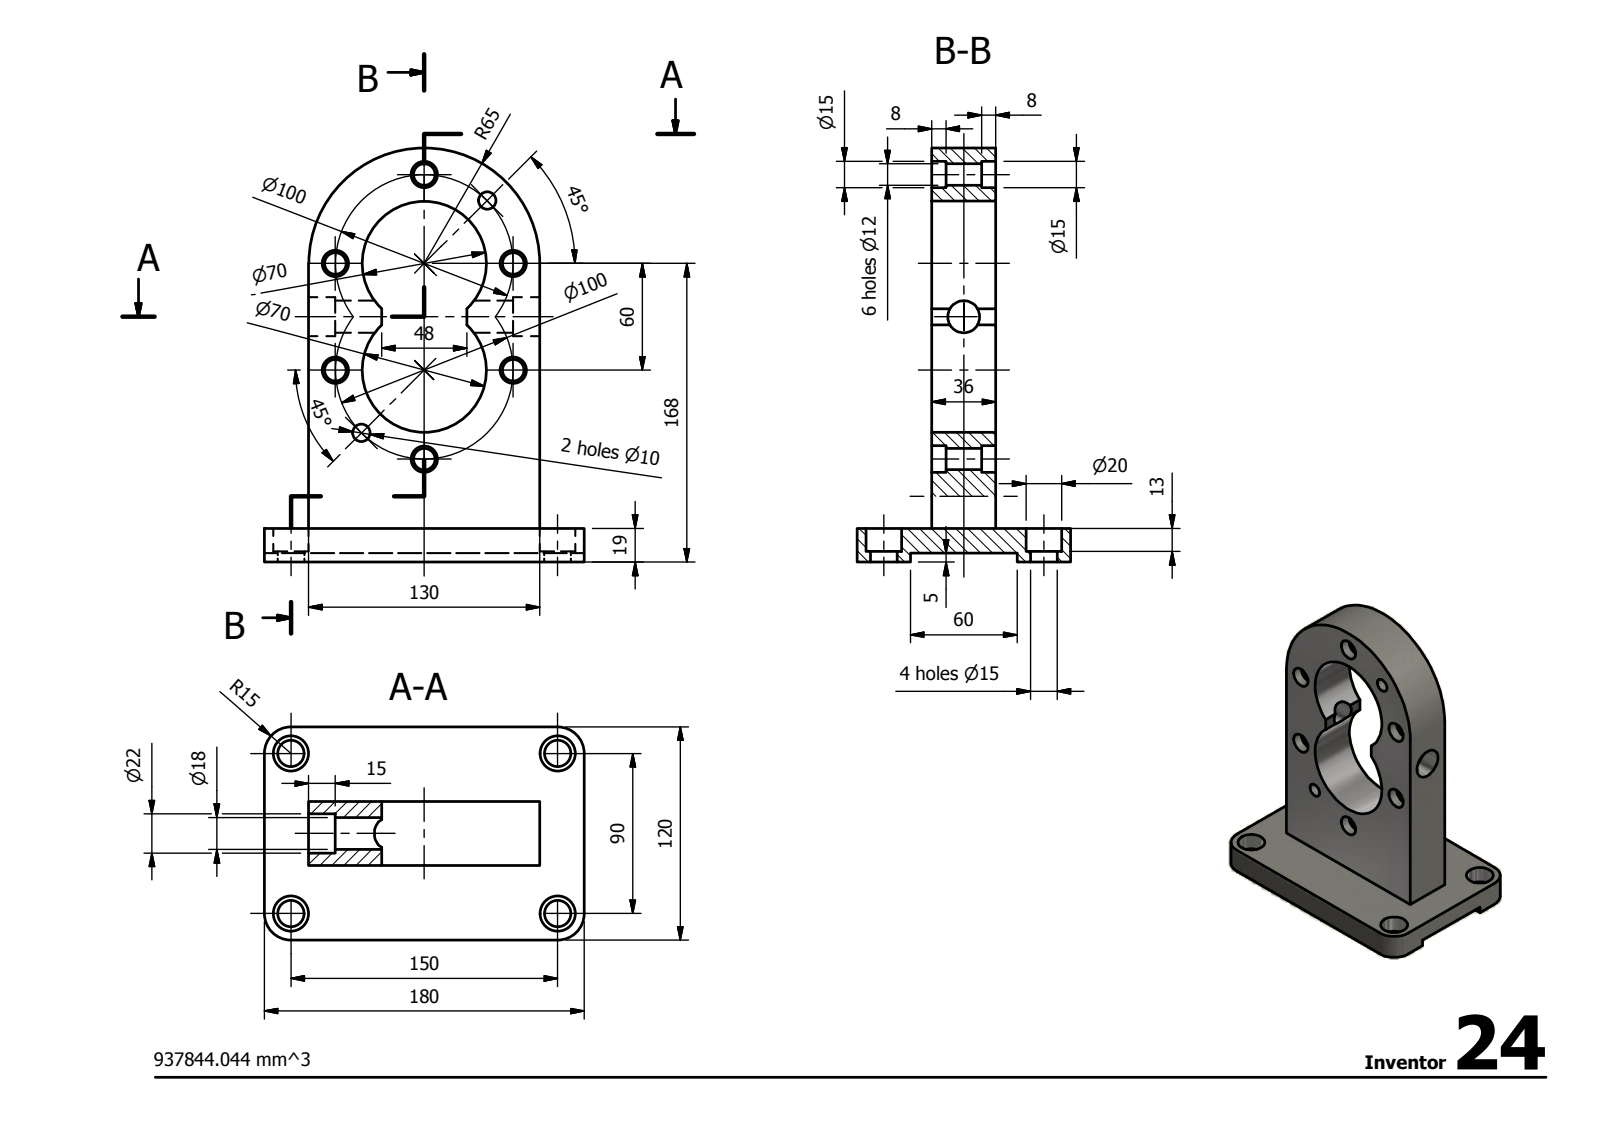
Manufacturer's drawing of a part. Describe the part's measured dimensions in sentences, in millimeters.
Its 3-D file was written by "Autodesk Inventor 2014 (AUTOMOTIVE_DESIGN)". It is 1 solid with 75 faces: 36 planar, 39 cylindrical and 0 other. Overall it measures 233 by 180 by 120 millimeters. Its volume is 937 805 cubic millimeters and its surface area 134 353 square millimeters. Round holes: 10 of diameter 15, 6 of diameter 12, 4 of diameter 20, 2 of diameter 10, 1 of diameter 18, 1 of diameter 22. Partial cylindrical surfaces (rounded edges, fillets, slot ends): 4 of radius 15, 2 of radius 35, 1 of radius 65. The main face-to-face distances are 36, 14, 5, 19, 42, 78, 130, 120, 25, 155. The hole center spacings are 38.27, 70.71, 120.83, 60, 90, 92.39, 96.48, 100.
